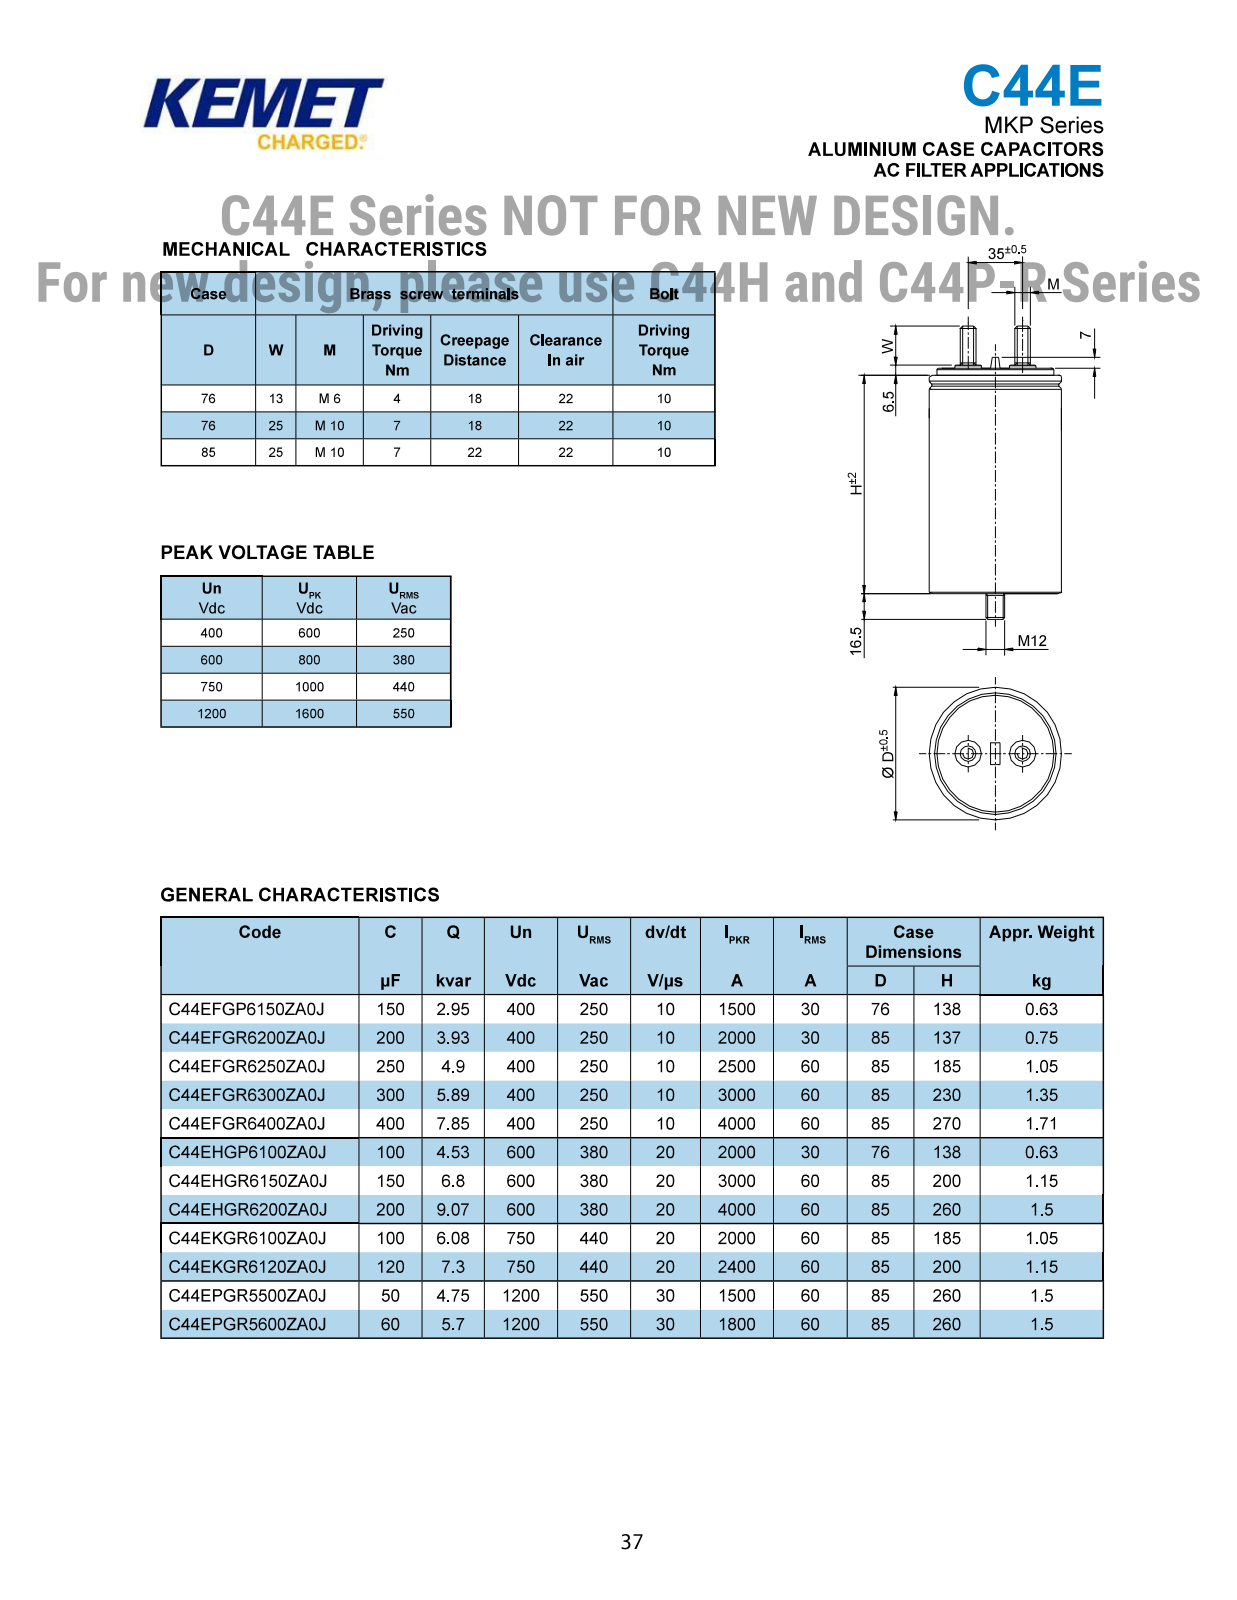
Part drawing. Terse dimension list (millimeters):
name: CFP_C44E_85X270_D85.5L272S35.5LL25
written by: SolidWorks 2014 (AUTOMOTIVE_DESIGN)
unit: mm
bodies: 1 solid, 103 faces (34 planar, 34 cylindrical, 35 other)
size: 319.5 × 85.51 × 85.5
volume: 1 582 000 mm³; area: 89 185 mm²
bosses: 2× ⌀15, 2× ⌀10, 1× ⌀85.5, 1× ⌀68, 1× ⌀12
rounds: 1× R42.76
face distances: 276, 272, 4, 278.5, 6.5, 2.5, 283, 11, 7, 4.5
